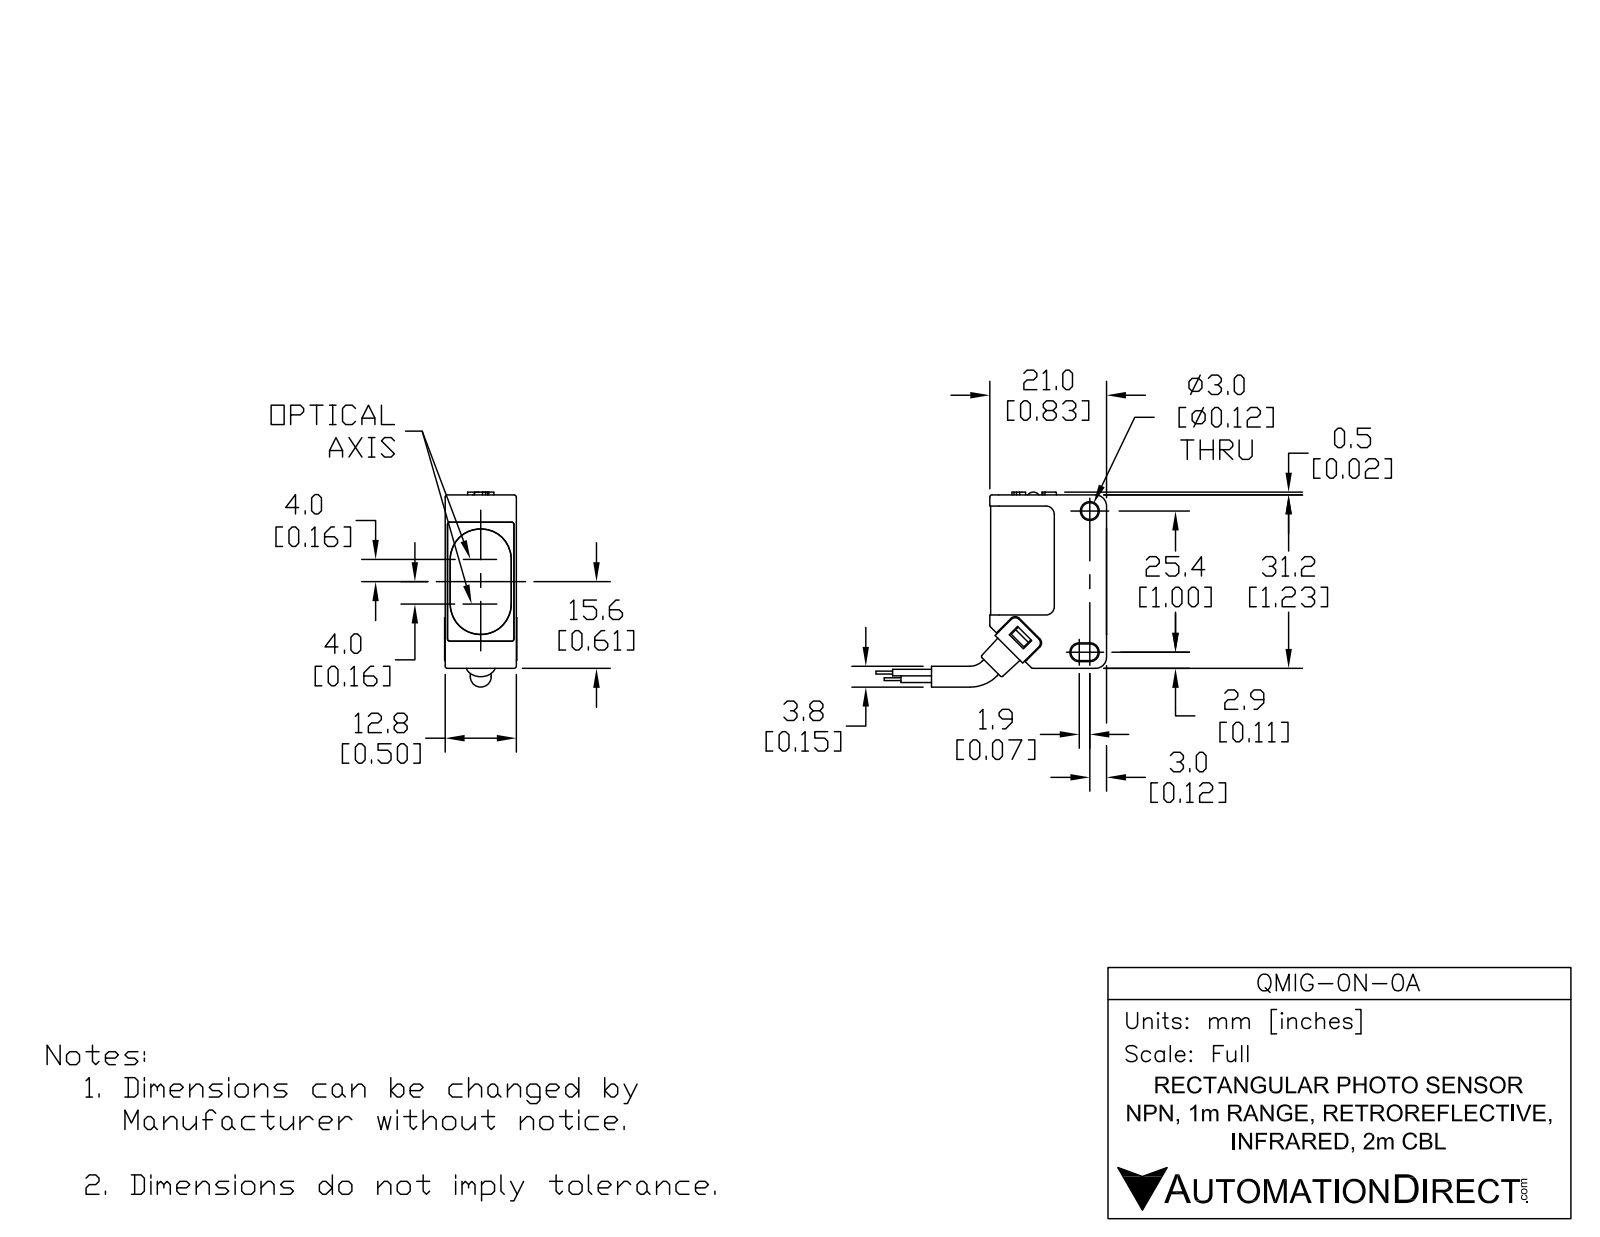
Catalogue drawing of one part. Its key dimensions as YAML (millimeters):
part_name: "QMIG-0N-0A"
step_written_by: "SolidWorks 2017 (AUTOMOTIVE_DESIGN)"
units: millimeters
bodies: {solids: 9, faces: 258, planar: 134, cylindrical: 100, other: 24}
overall_size: [81.1, 26.2, 13]
volume: 7700
surface_area: 5403
round_holes:
  - {diameter: 3, count: 3}
  - {diameter: 3.8, count: 1}
  - {diameter: 5.7, count: 1}
  - {diameter: 7.2, count: 1}
round_bosses_or_shafts:
  - {diameter: 3.5, count: 2}
partial_cylinders:
  - {radius: 0.4, count: 13}
  - {radius: 0.5, count: 10}
  - {radius: 1, count: 8}
  - {radius: 1.5, count: 6}
  - {radius: 0.6, count: 4}
  - {radius: 0.2, count: 2}
  - {radius: 0.9, count: 2}
  - {radius: 1.1, count: 2}
face_to_face_distances: [0.5, 12.6, 1.5, 0.4, 12.8, 3.5, 12.4, 2, 12.2, 12.5]
hole_center_spacings: [5.2]
